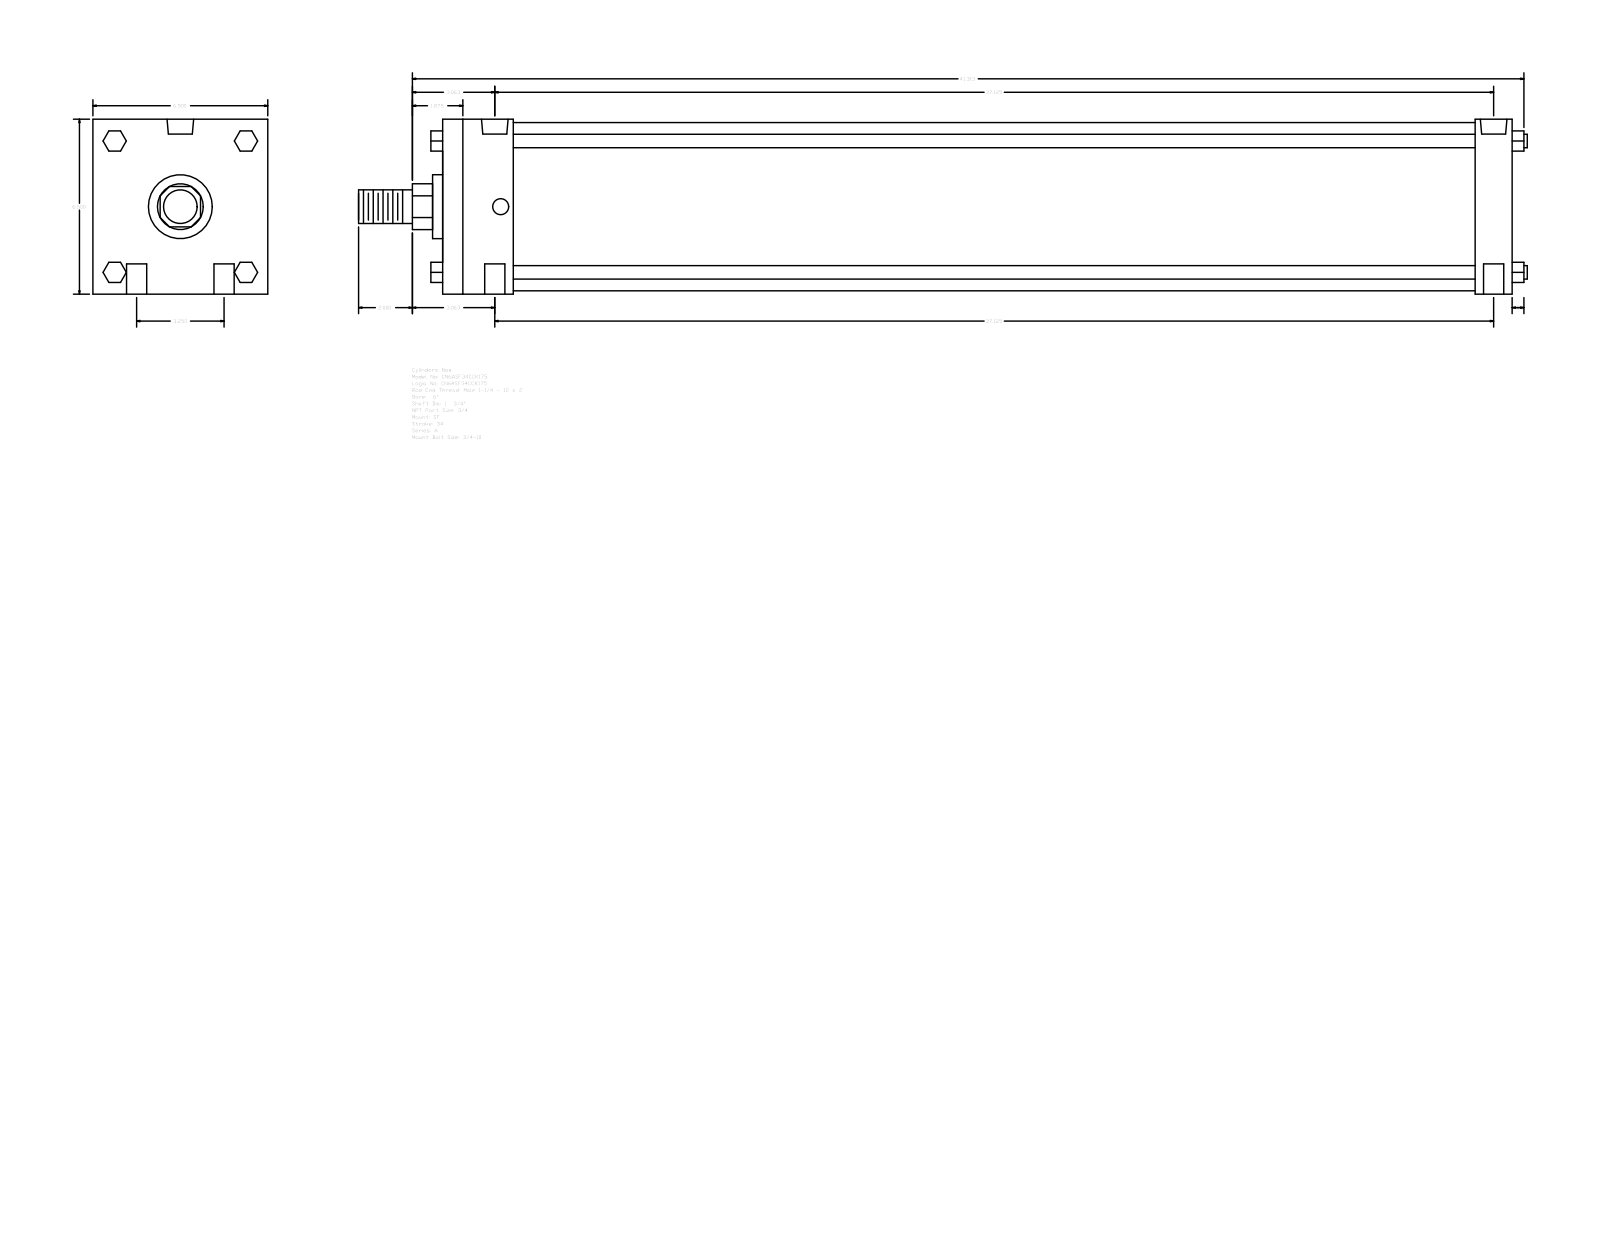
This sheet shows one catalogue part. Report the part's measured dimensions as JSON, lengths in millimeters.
{"part_name": "A_SF__0600_1.75", "step_written_by": "GSSL Pune (CONFIG_CONTROL_DESIGN)", "units": "millimeters", "bodies": {"solids": 0, "faces": 124, "planar": 94, "cylindrical": 30, "other": 0}, "overall_size": [1103.31, 165.1, 165.1], "round_holes": [[19.05, 4], [15.08, 2], [25.12, 2]], "round_bosses_or_shafts": [[12.7, 4], [158.75, 1], [60.33, 1], [44.45, 1], [31.75, 1]], "partial_cylinders_radius": [[21.63, 1]], "face_to_face_distances": [165.1, 1009.65, 66.68, 974.73, 34.92, 908.05, 942.97, 19.05, 61.97, 107.34], "hole_center_spacings": [41.27, 943.87, 942.97, 82.54, 946.58, 931.85]}
